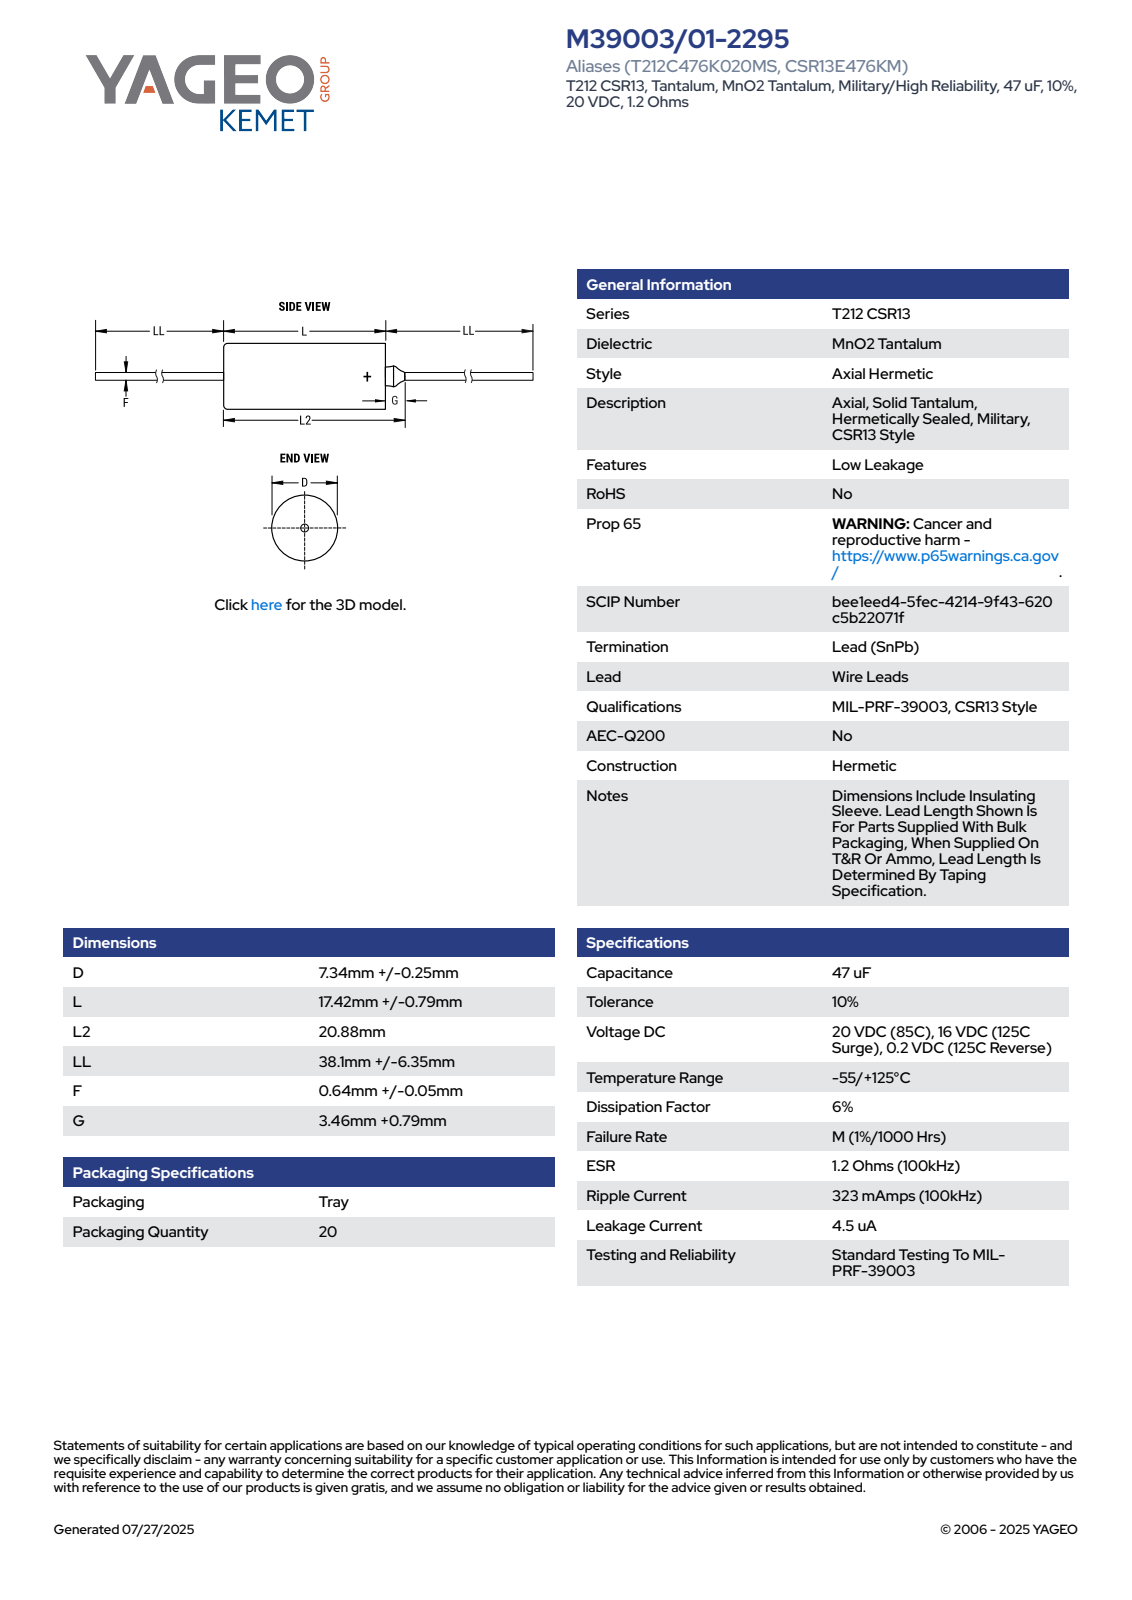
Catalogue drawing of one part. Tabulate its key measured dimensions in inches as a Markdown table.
| quantity | value |
| --- | --- |
| part name | CTAM_AHTWG_D7.59L18.21L220.88LL44.45F0.69G4.25 |
| STEP written by | SolidWorks 2014 (AUTOMOTIVE_DESIGN) |
| units | inches |
| bodies | 1 solid, 98 faces (29 planar, 30 cylindrical, 39 other) |
| overall size | 4.217 × 0.299 × 0.299 |
| volume | 0.041 in³ |
| surface area | 1.3 in² |
| round holes (diameter × count) | 0.283 × 1 |
| round bosses / shafts (diameter × count) | 0.299 × 1, 0.052 × 1, 0.051 × 1, 0.027 × 1 |
| partial cylindrical surfaces (radius × count) | 0.149 × 1 |
| main face-to-face distances | 0.532, 0.71, 0.178, 1.757, 2.289, 2.467, 4.217, 2.46, 1.928, 1.75 |
